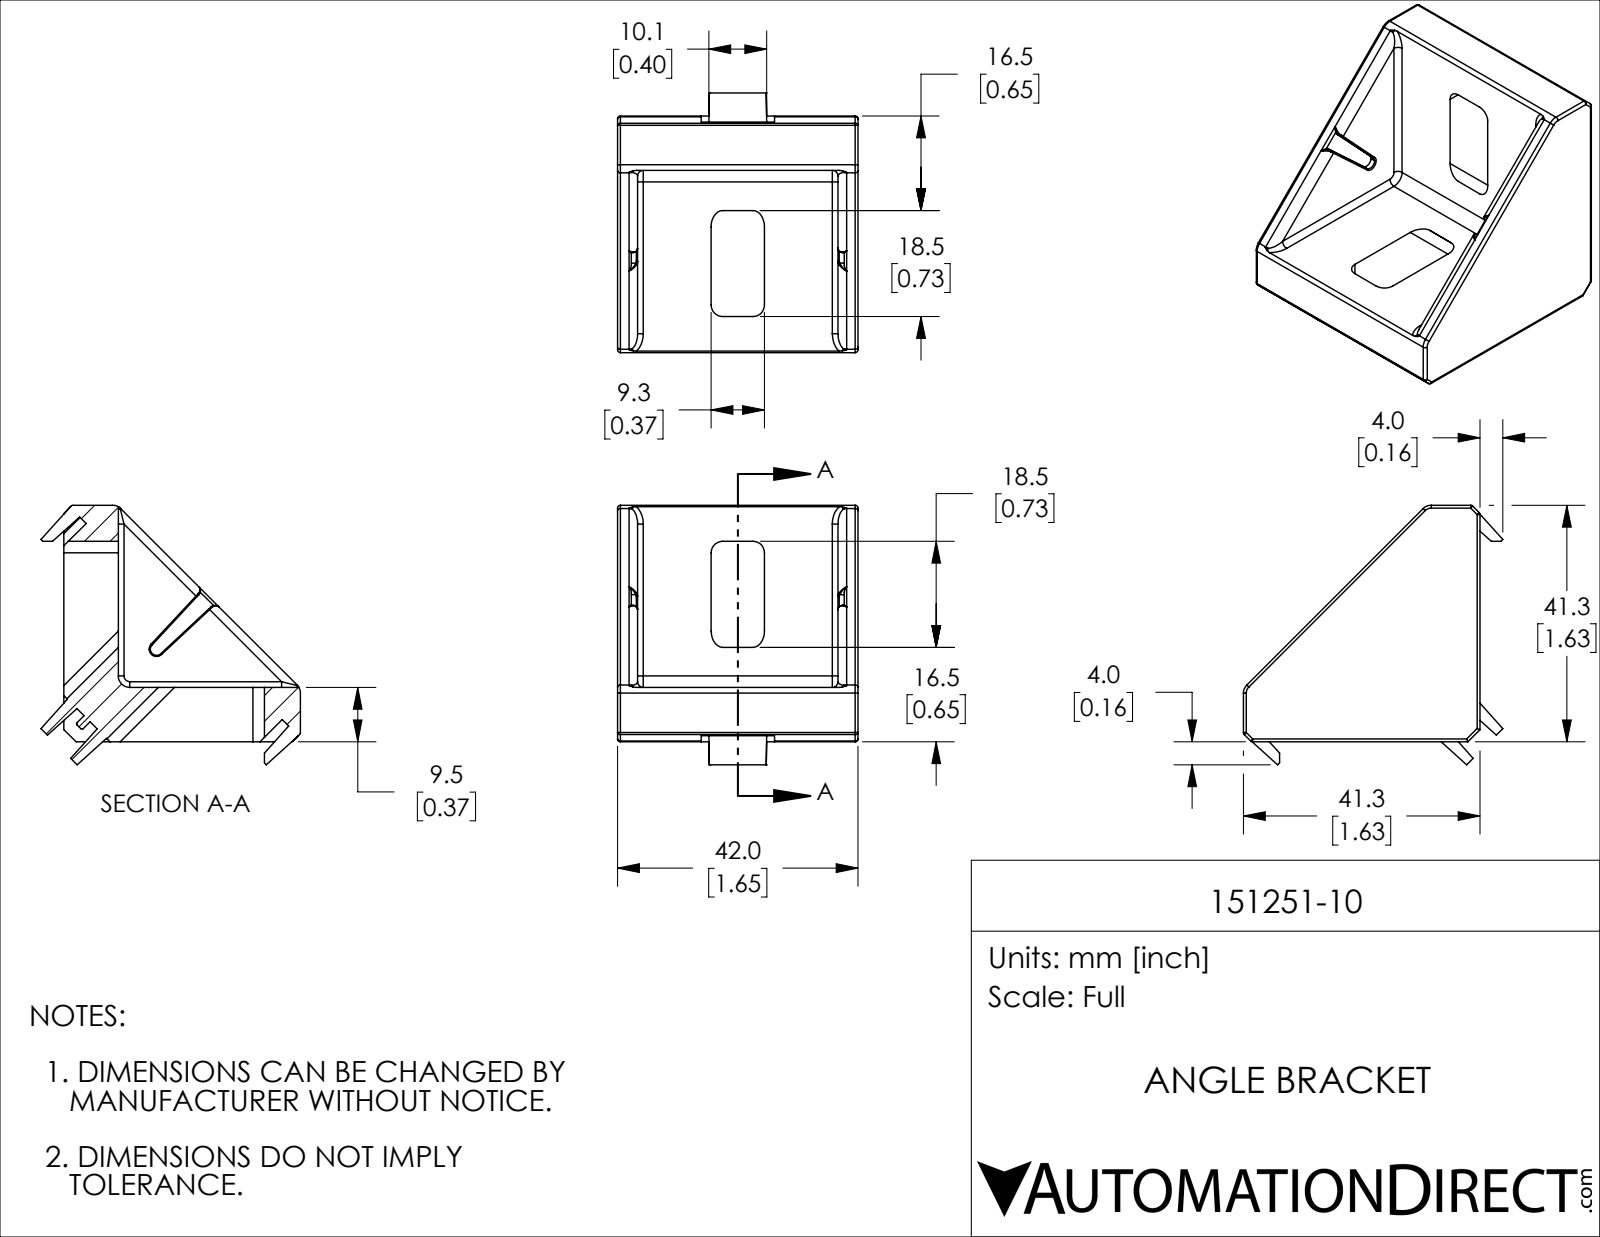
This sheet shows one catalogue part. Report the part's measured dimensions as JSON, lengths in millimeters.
{"part_name": "151251-10", "step_written_by": "SolidWorks 2024 (CONFIG_CONTROL_DESIGN)", "units": "millimeters", "bodies": {"solids": 1, "faces": 224, "planar": 97, "cylindrical": 90, "other": 37}, "overall_size": [45.3, 45.3, 42], "volume_mm3": 20339, "surface_area_mm2": 13494, "round_bosses_or_shafts": [[6, 8]], "partial_cylinders_radius": [[2, 25], [0.5, 22], [1, 6], [0.2, 4], [1.5, 4], [0.3, 2], [1.08, 1]], "face_to_face_distances": [9.5, 42, 3, 13, 10, 6.7, 2.8, 25.5, 29, 39]}
